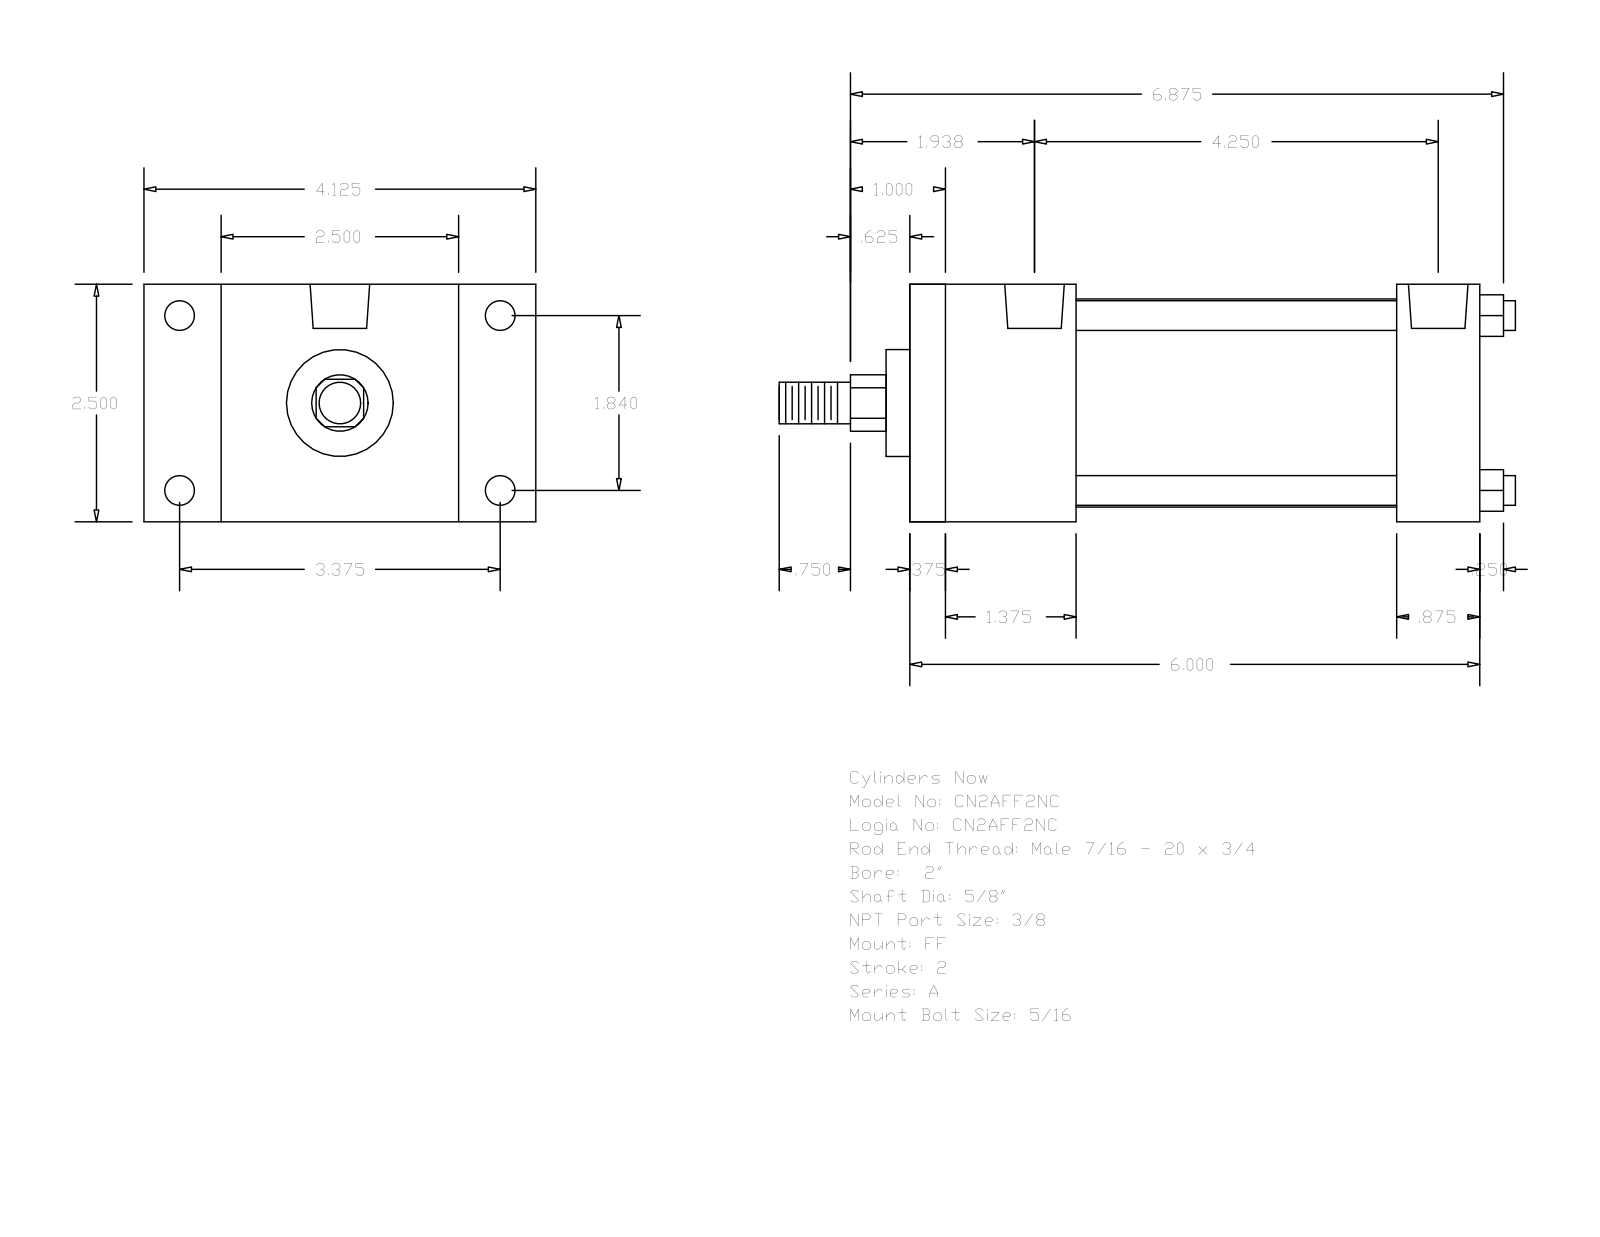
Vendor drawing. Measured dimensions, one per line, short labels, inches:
name: A_FF__0200_0.625
written by: GSSL Pune (CONFIG_CONTROL_DESIGN)
unit: in
bodies: 0 solids, 92 faces (64 planar, 28 cylindrical, 0 other)
size: 7.75 × 4.125 × 2.5
holes: 4× ⌀0.219, 4× ⌀0.313, 2× ⌀0.627
bosses: 4× ⌀0.313, 1× ⌀2.19, 1× ⌀1.125, 1× ⌀0.625, 1× ⌀0.437
rounds: 1× R0.297
face distances: 2.5, 6, 0.375, 5.625, 1.375, 1.75, 5.125, 4.75, 3.375, 4.25
hole spacings: 1.84, 3.375, 3.844, 3.937, 0.156, 0.157, 4.093, 4.094
